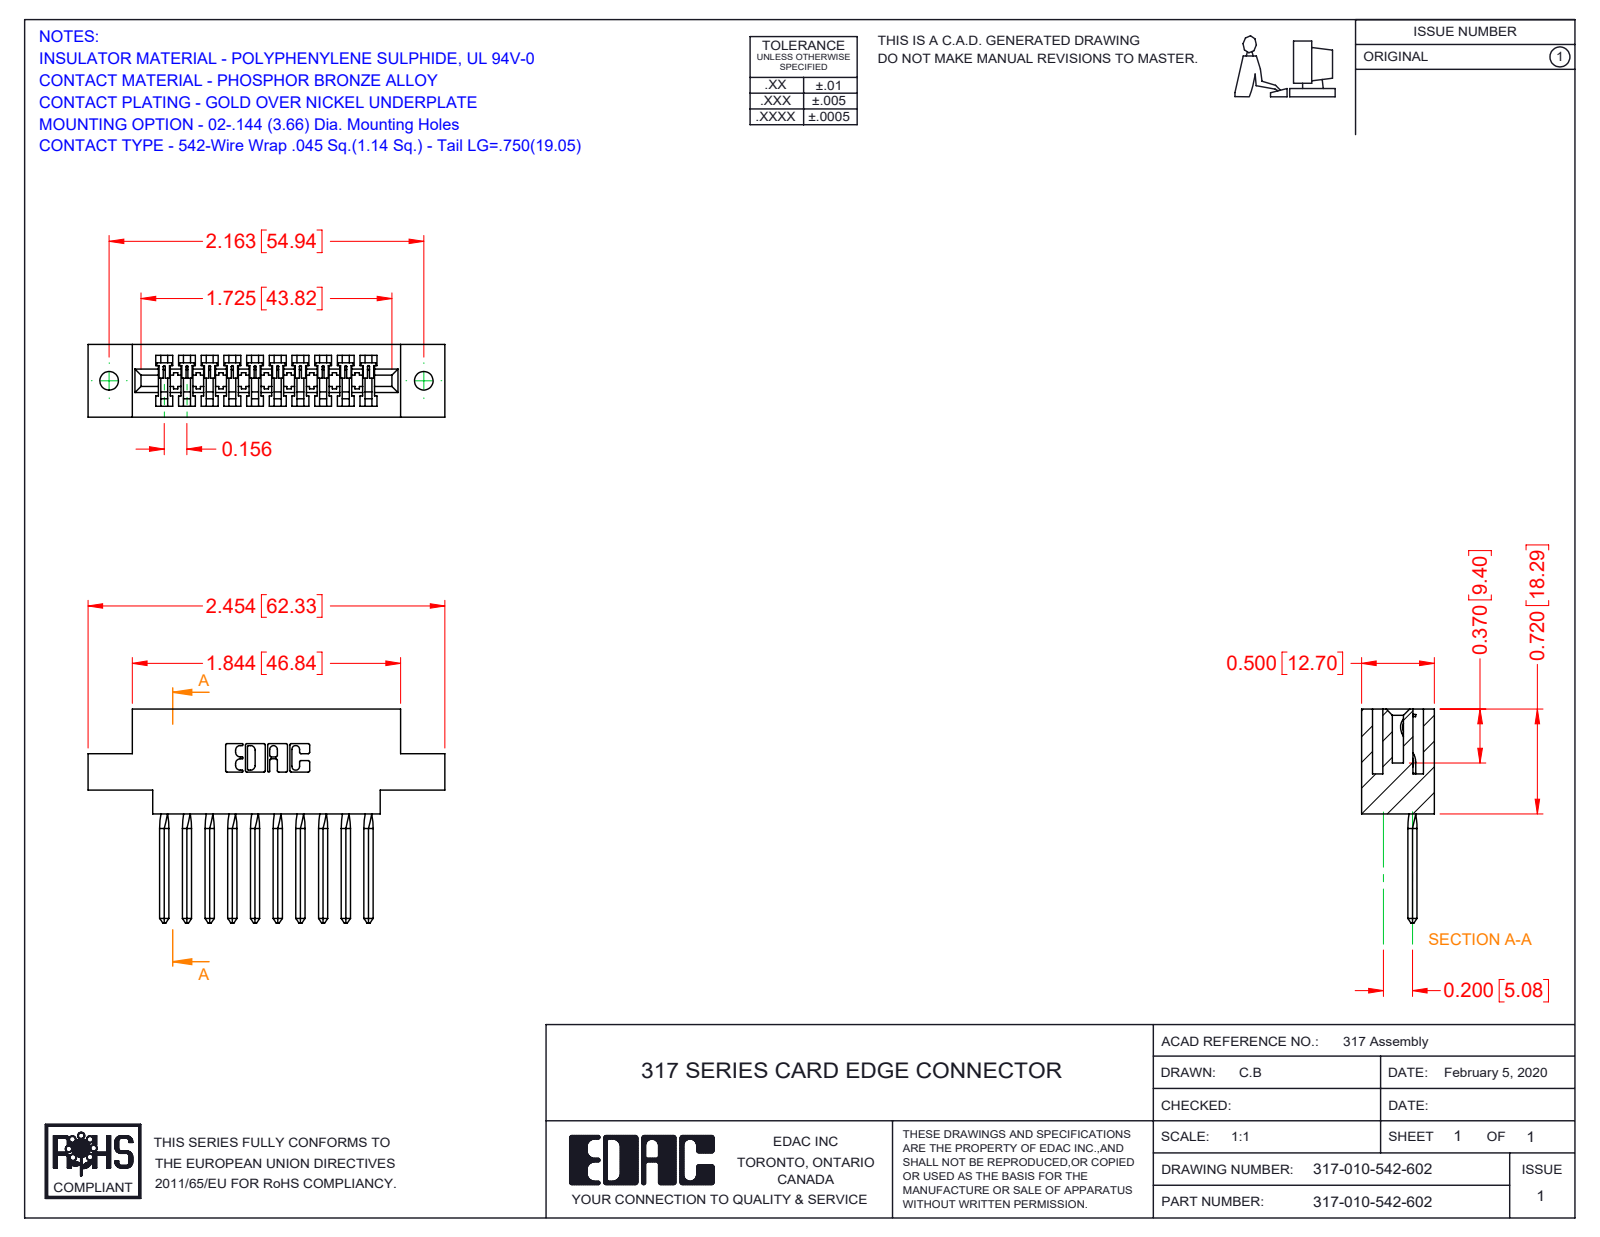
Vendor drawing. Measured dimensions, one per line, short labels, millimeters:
name: 317-010-542-602; 317 Part_.144 Dia; 317-290-003_542
written by: SolidWorks 2016 (CONFIG_CONTROL_DESIGN)
unit: mm
bodies: 11 solids, 852 faces (698 planar, 114 cylindrical, 40 other)
size: 62.3 × 37.3 × 12.7
volume: 8 730 mm³; area: 9 677 mm²
holes: 2× ⌀3.3
rounds: 22× R0.3, 20× R0.2, 6× R0.2, 6× R0.8, 3× R0.7, 1× R1.9, 1× R2.3, 1× R2.5
face distances: 12.7, 1.9, 10.8, 2.8, 1.7, 5.6, 8.9, 8.4, 4, 2.9
hole spacings: 54.9
